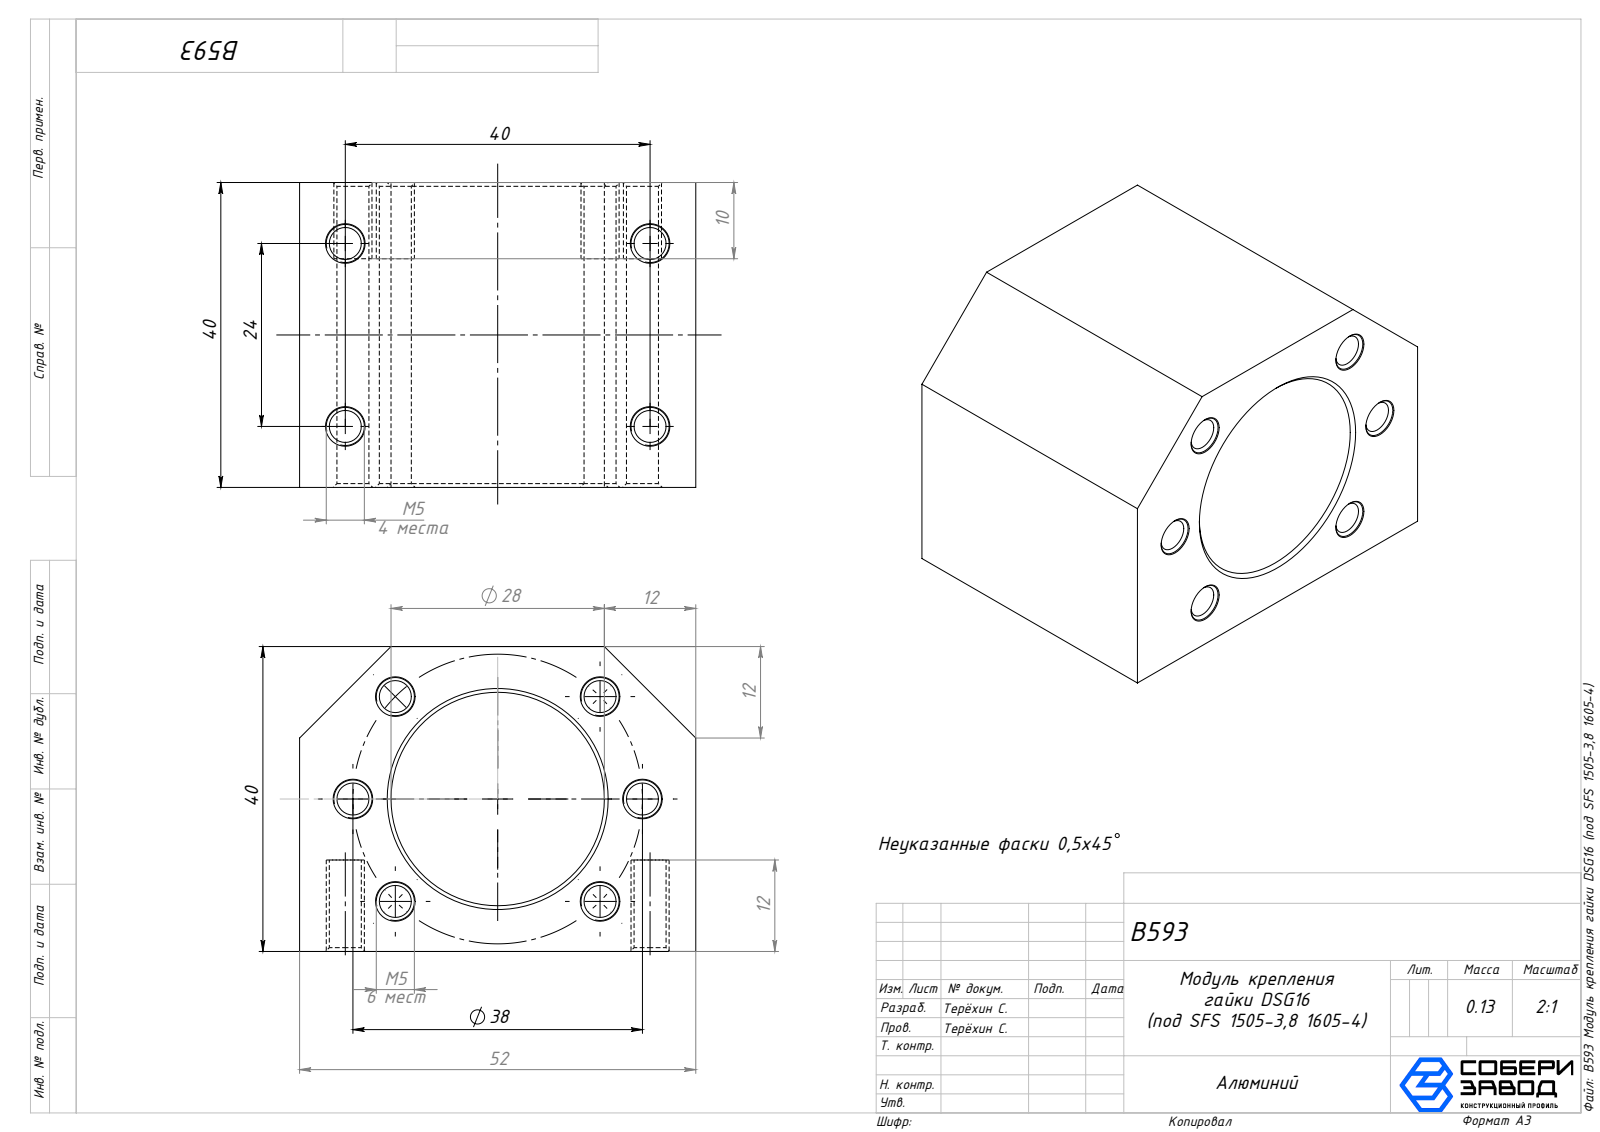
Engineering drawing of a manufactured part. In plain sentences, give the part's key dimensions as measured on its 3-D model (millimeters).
The part is named "B593 Модуль крепления гайки DSG16 (под SFS 1505-3,8 1605-4)_DSG16H; Сборка2". Its 3-D file was written by "SolidWorks 2025 (AUTOMOTIVE_DESIGN)". It is 1 solid with 70 faces: 12 planar, 22 cylindrical and 36 other. Overall it measures 52 by 40 by 40 millimeters. Its volume is 48 769 cubic millimeters and its surface area 16 483 square millimeters. Round holes: 10 of diameter 4.2, 1 of diameter 28. The main face-to-face distances are 40, 52, 12, 28. The hole center spacings are 19, 26.87, 14.54, 38, 24, 35.1, 35.11, 40.
